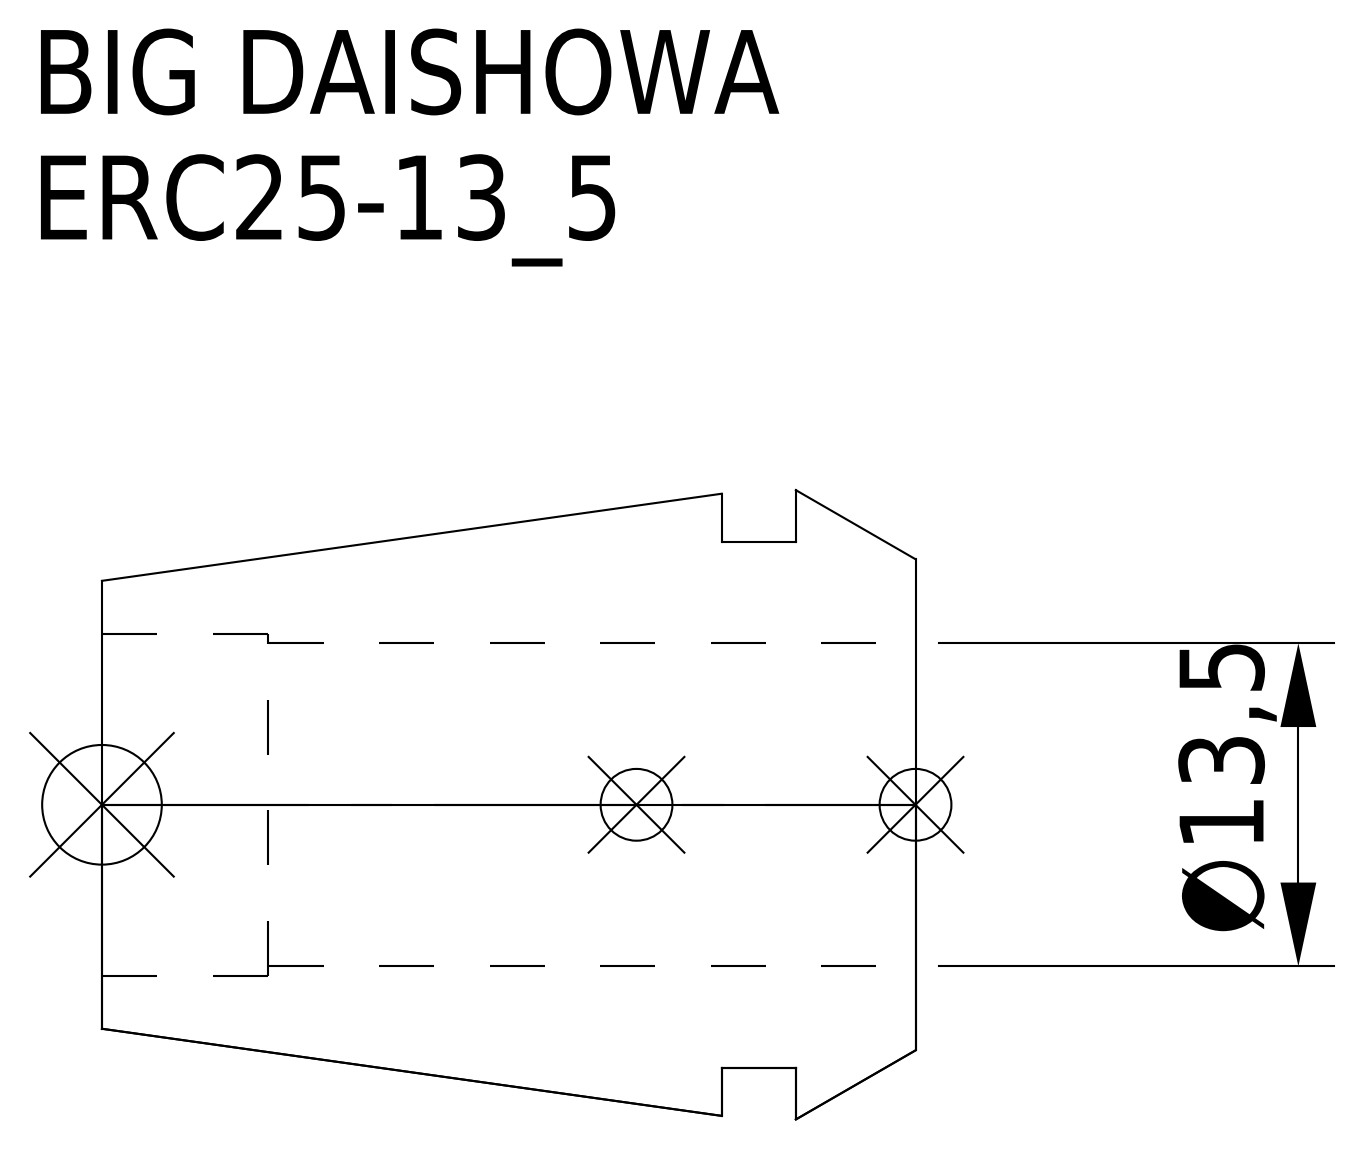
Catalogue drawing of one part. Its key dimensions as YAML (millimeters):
part_name: "ERC25-13_5"
step_written_by: "CREO PARAMETRIC BY PTC INC, 2016380 (AUTOMOTIVE_DESIGN)"
units: millimeters
bodies: {solids: 1, faces: 15, planar: 5, cylindrical: 6, other: 4}
overall_size: [34, 26.3, 26.3]
volume: 8615
surface_area: 4570
round_holes:
  - {diameter: 13.5, count: 1}
  - {diameter: 14.3, count: 1}
round_bosses_or_shafts:
  - {diameter: 22, count: 1}
face_to_face_distances: [5, 8.1, 3.1, 34, 29, 25.9, 27.04, 22.04, 18.94, 6.96]
